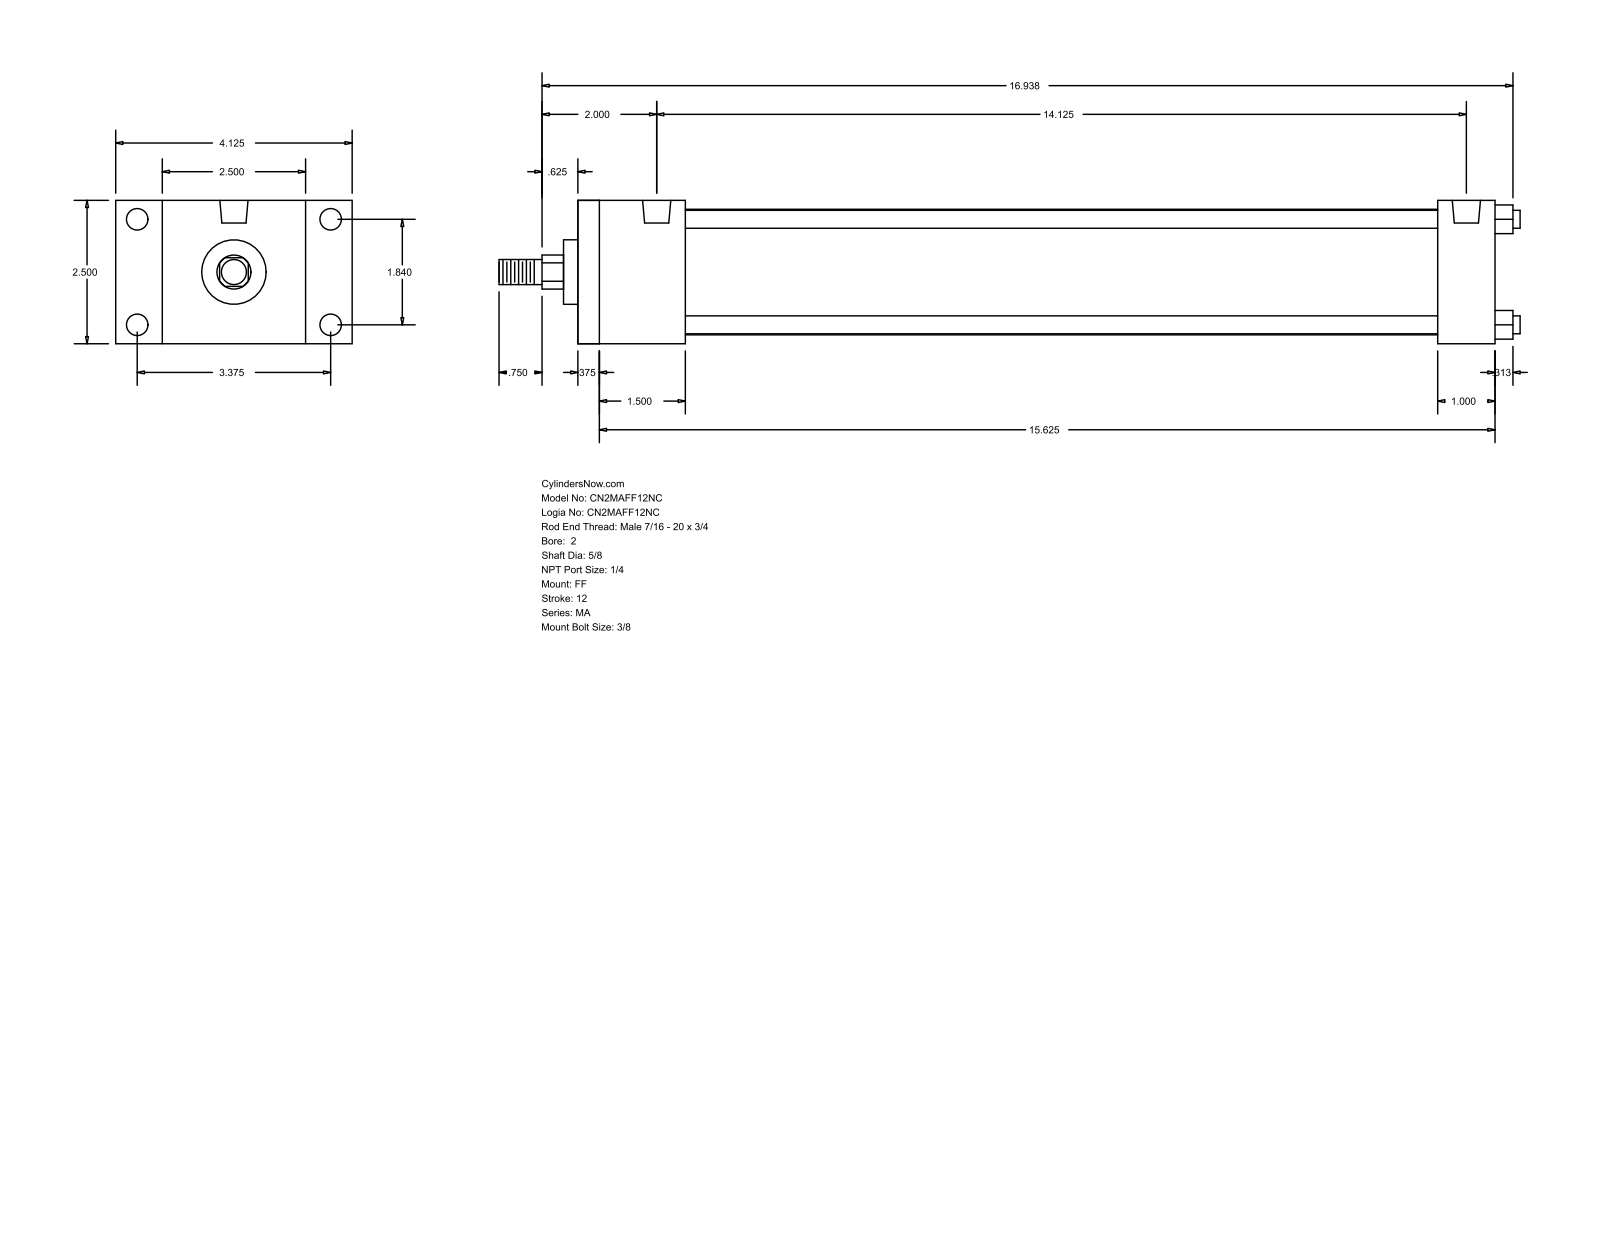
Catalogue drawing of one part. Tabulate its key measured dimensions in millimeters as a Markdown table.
| quantity | value |
| --- | --- |
| part name | MA_FF__0200_0.625 |
| STEP written by | GSSL Pune (CONFIG_CONTROL_DESIGN) |
| units | millimeters |
| bodies | 0 solids, 92 faces (64 planar, 28 cylindrical, 0 other) |
| overall size | 452.44 × 104.78 × 63.5 |
| round holes (diameter × count) | 7.94 × 4, 9.53 × 4, 12.49 × 2 |
| round bosses / shafts (diameter × count) | 7.94 × 4, 55.63 × 1, 28.57 × 1, 15.88 × 1, 11.11 × 1 |
| partial cylindrical surfaces (radius × count) | 7.54 × 1 |
| main face-to-face distances | 63.5, 406.39, 9.52, 396.87, 38.1, 47.62, 381, 371.48, 333.38, 358.77 |
| hole center spacings | 46.74, 85.72, 97.63, 358.77 |
